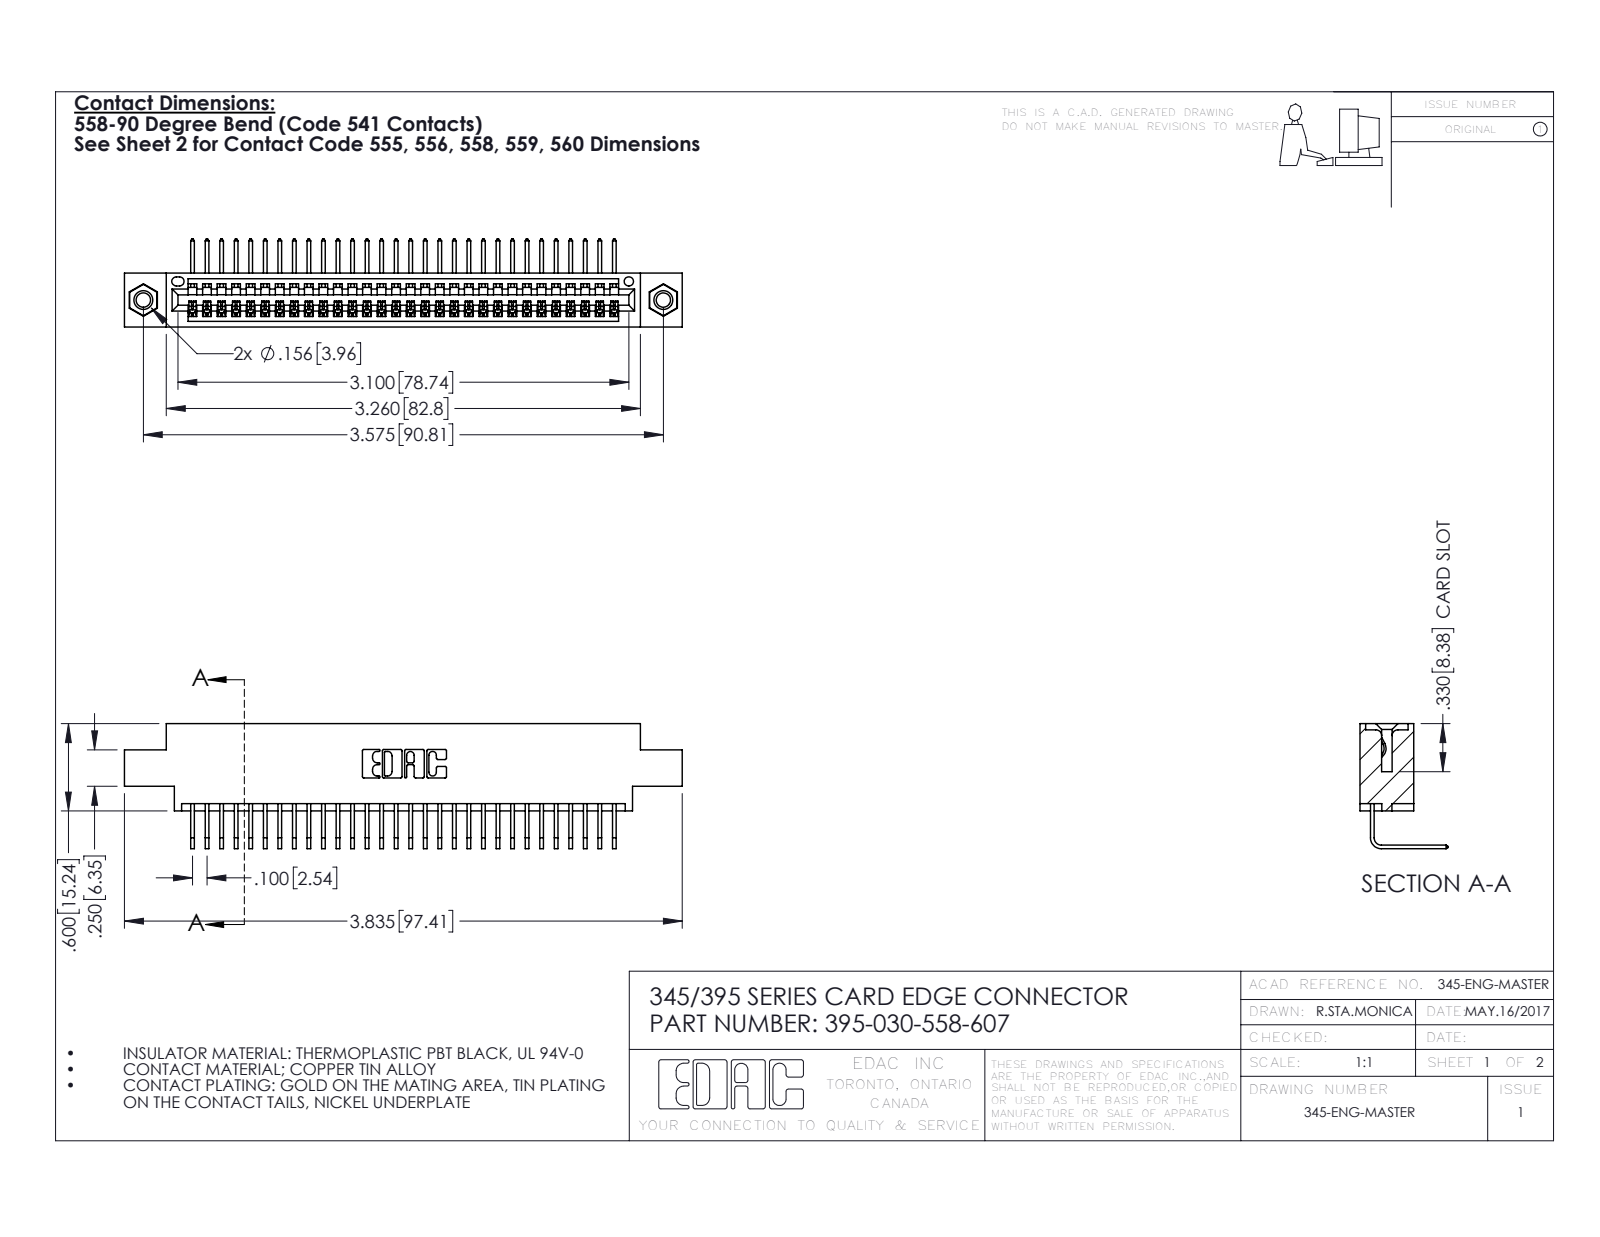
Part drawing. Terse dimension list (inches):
name: 345 Part_0.170 Offset - 0.156 Dia-TI; 395-030-558-607; 345-250-001_345-250-005-103; 345-292-001_558 Tail - 2
written by: SolidWorks 2016 (CONFIG_CONTROL_DESIGN)
unit: in
bodies: 33 solids, 1990 faces (1376 planar, 598 cylindrical, 16 other)
size: 3.835 × 0.859 × 0.605
volume: 0.557 in³; area: 19.7 in²
holes: 2× ⌀0.098, 2× ⌀0.125, 2× ⌀0.156, 1× ⌀0.064
bosses: 2× ⌀0.155
rounds: 60× R0.006, 22× R0.01, 6× R0.007, 6× R0.031, 3× R0.026, 2× R0.031, 2× R0.04, 1× R0.014
face distances: 0.072, 0.298, 0.37, 0.2, 0.098, 0.272, 0.025, 0.225, 0.175, 0.149
hole spacings: 0.27, 3.34, 3.575
